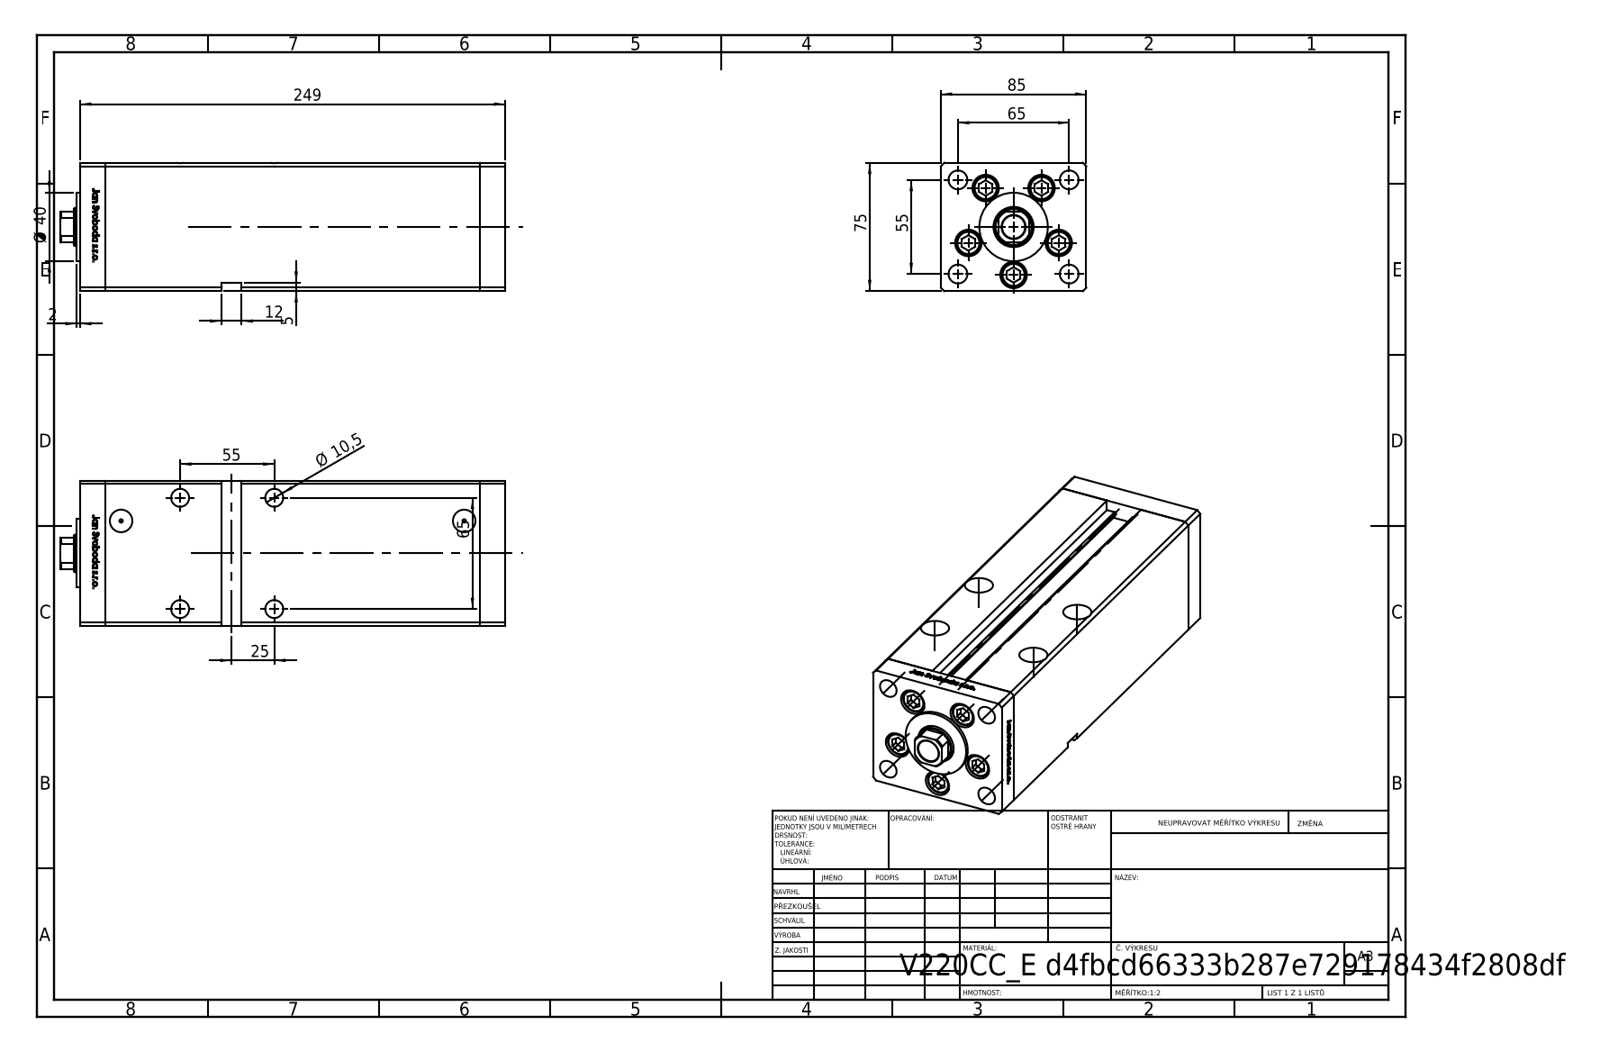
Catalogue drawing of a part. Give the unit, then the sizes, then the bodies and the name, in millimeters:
Units: millimetres
Overall size (bounding box): 260 × 85 × 75
Round holes (diameter × count): ⌀11 ×9, ⌀15.5 ×5, ⌀10.5 ×4, ⌀16.5 ×4, ⌀2 ×2, ⌀13.16 ×2, ⌀13.5 ×1, ⌀22 ×1, ⌀23.5 ×1
Round bosses / shafts (diameter × count): ⌀14.5 ×5, ⌀8 ×5, ⌀40 ×1
Partial cylindrical surfaces — rounded edges, fillets, slot ends (radius × count): R0.93 ×2, R10.5 ×1
Main face-to-face distances: 85, 75, 15, 218.5, 233.5, 248.5, 10.5, 64.5, 34.25, 68.5
Hole centre spacings: 28, 42.57, 55, 65, 85.15, 16.86, 19.17, 32.33
Volume: 1 341 000 mm³ · Surface area: 209 571 mm²
Bodies: 14 solids, 1214 faces (475 planar, 165 cylindrical, 574 other)
Part name (STEP PRODUCT): V220C BACK_E; V220C_VC_E; ALLEN BOLT; V220C_E MIDDLE (+1 more)
STEP written by: SolidWorks 2019 (CONFIG_CONTROL_DESIGN)
